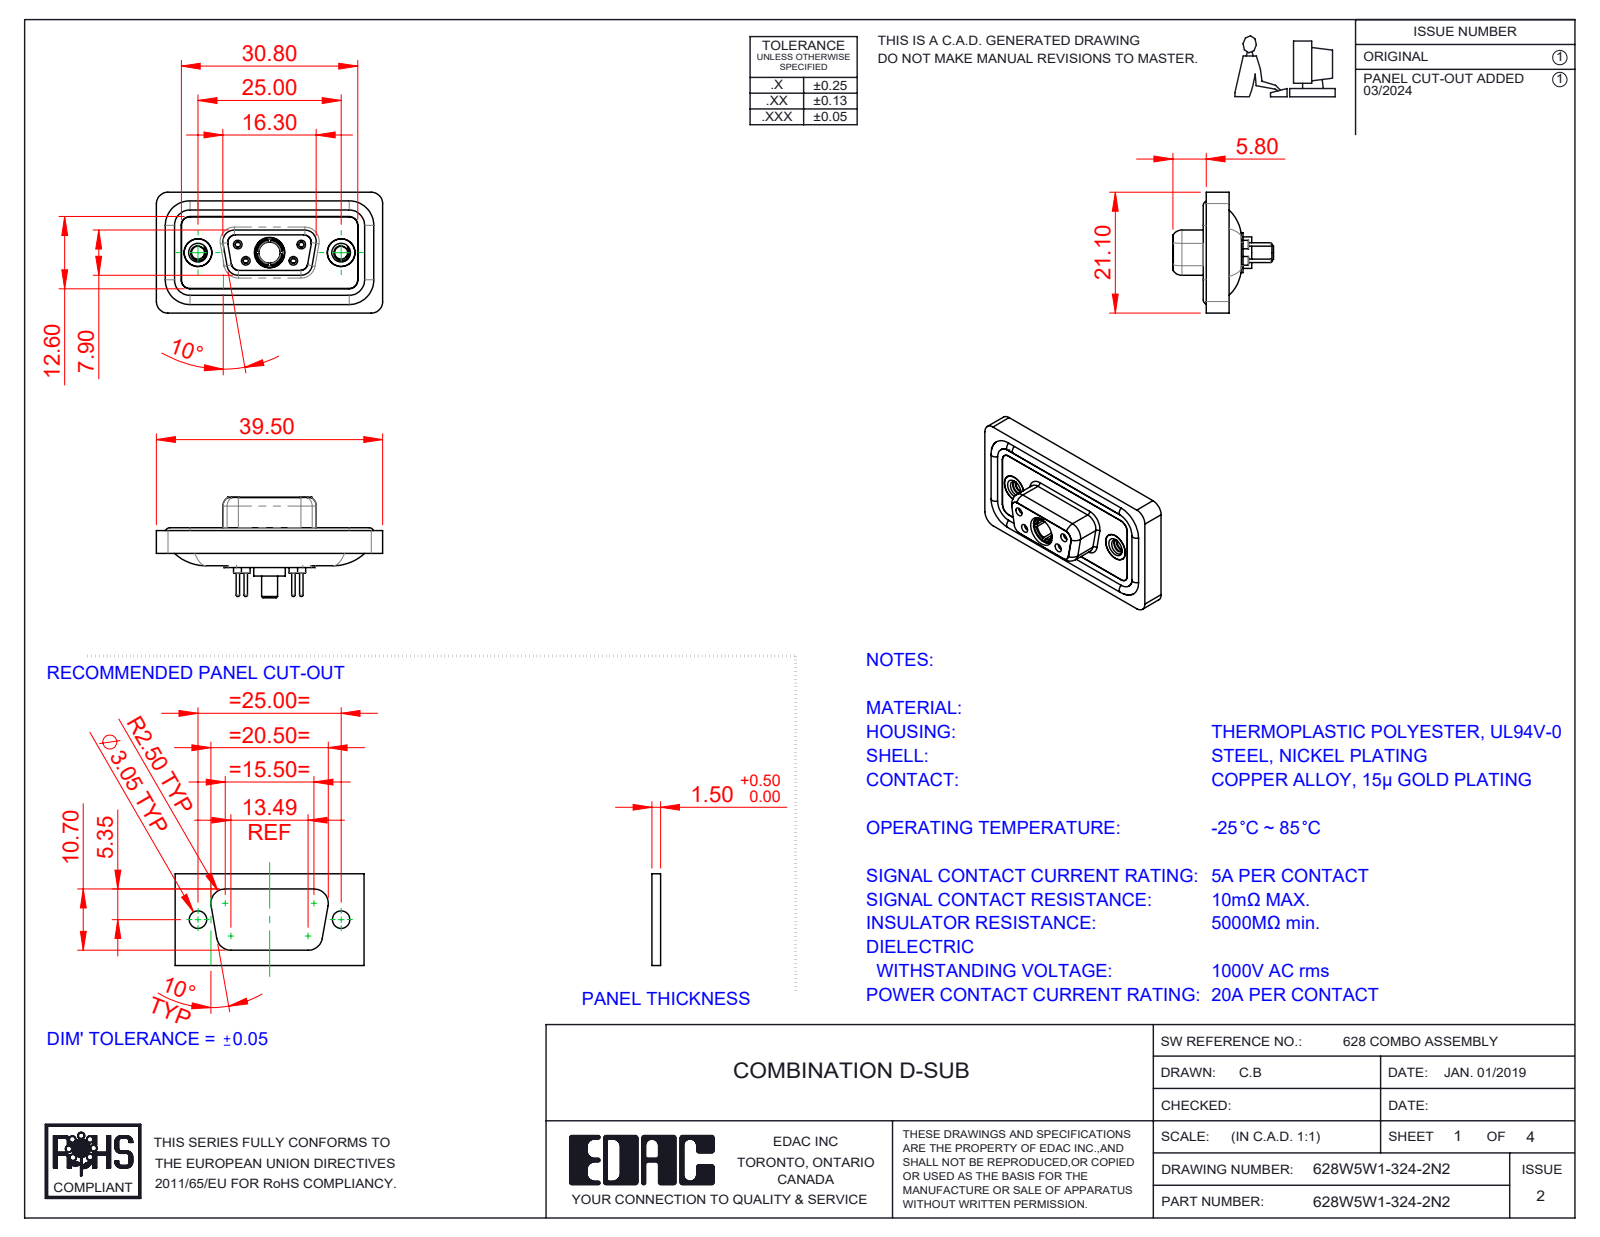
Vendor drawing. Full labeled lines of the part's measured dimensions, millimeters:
Part name (STEP PRODUCT): 628Combo Housing_5W1; 628Combo Shell Rear_09 Contacts; 628Combo Waterproof Housing_09 Contacts; 628Combo Shell Front_09 Contacts (+5 more)
STEP written by: SolidWorks 2023 (CONFIG_CONTROL_DESIGN)
Units: millimetres
Bodies: 13 solids, 680 faces (194 planar, 287 cylindrical, 199 other)
Overall size (bounding box): 39.5 × 21.1 × 17.55
Volume: 4 767 mm³ · Surface area: 7 635 mm²
Round holes (diameter × count): ⌀0.9 ×4, ⌀1.1 ×4, ⌀1.5 ×4, ⌀2 ×4, ⌀4.85 ×3, ⌀1.6 ×2, ⌀1.7 ×2, ⌀2.26 ×2, ⌀4 ×2, ⌀4.05 ×2, ⌀5 ×2, ⌀3.7 ×1
Round bosses / shafts (diameter × count): ⌀1.6 ×6, ⌀2.2 ×4, ⌀0.6 ×4, ⌀4.95 ×2, ⌀4.8 ×2, ⌀5.5 ×1, ⌀5.2 ×1, ⌀4.96 ×1
Partial cylindrical surfaces — rounded edges, fillets, slot ends (radius × count): R1.5 ×22, R2 ×18, R1.35 ×8, R1.6 ×8, R0.25 ×4, R0.5 ×4, R0.6 ×4, R0.65 ×4
Main face-to-face distances: 0.4, 2.9, 1.1, 1.8, 1.6, 0.5, 5.65, 7.45, 5.35, 6.6
Hole centre spacings: 3.16, 5.72, 7.1, 12.5, 18.1, 4.39, 4.4, 8.31
